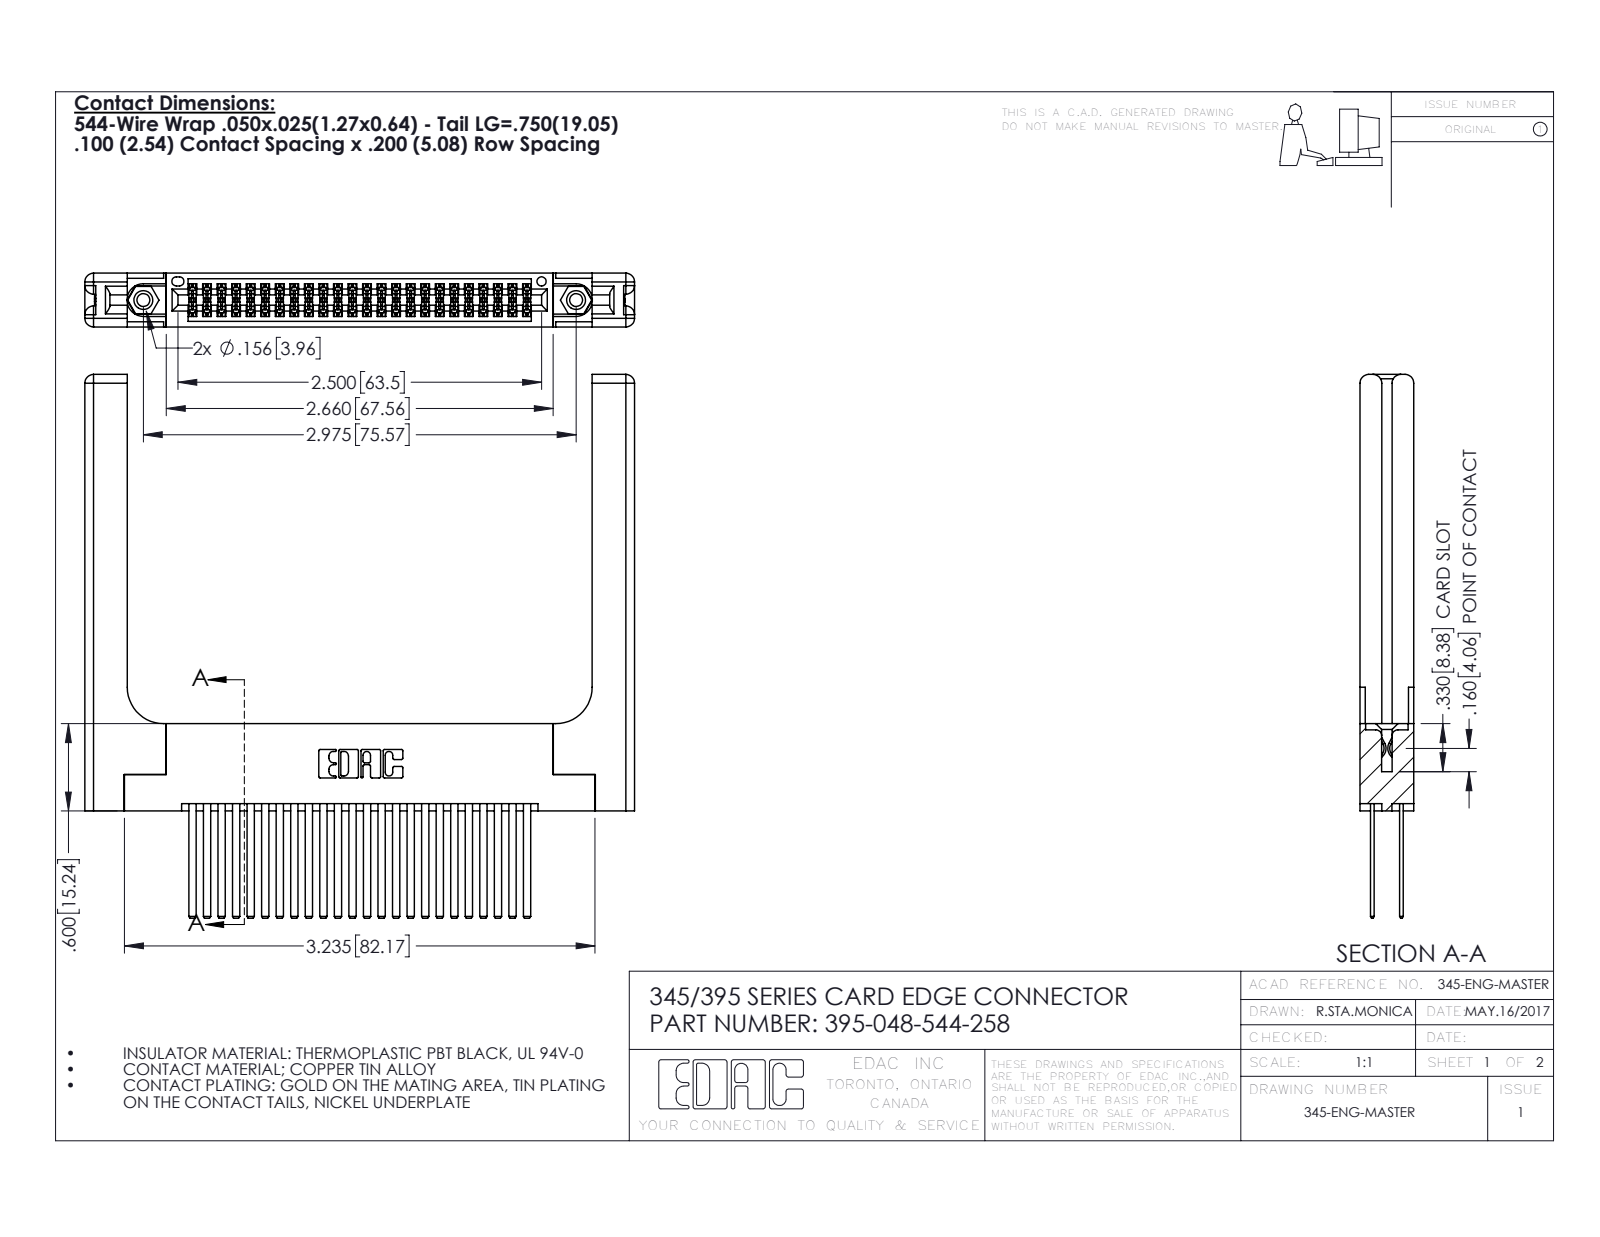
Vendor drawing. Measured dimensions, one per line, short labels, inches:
name: 395-048-544-258; 345-292-001_345-293-144; 345-220-058_345-220-058; 345-250-001_345-250-001-102 (+1 more)
written by: SolidWorks 2016 (CONFIG_CONTROL_DESIGN)
unit: in
bodies: 53 solids, 2494 faces (1620 planar, 814 cylindrical, 60 other)
size: 3.779 × 3.737 × 0.37
volume: 1.117 in³; area: 32.88 in²
holes: 2× ⌀0.089, 2× ⌀0.125, 2× ⌀0.156, 1× ⌀0.064
bosses: 2× ⌀0.155
rounds: 72× R0.006, 22× R0.01, 16× R0.06, 6× R0.007, 6× R0.031, 3× R0.026, 2× R0.014, 2× R0.019
face distances: 0.072, 0.298, 0.2, 0.37, 0.098, 0.272, 0.025, 0.225, 0.175, 0.148
hole spacings: 0.27, 2.741, 2.975
